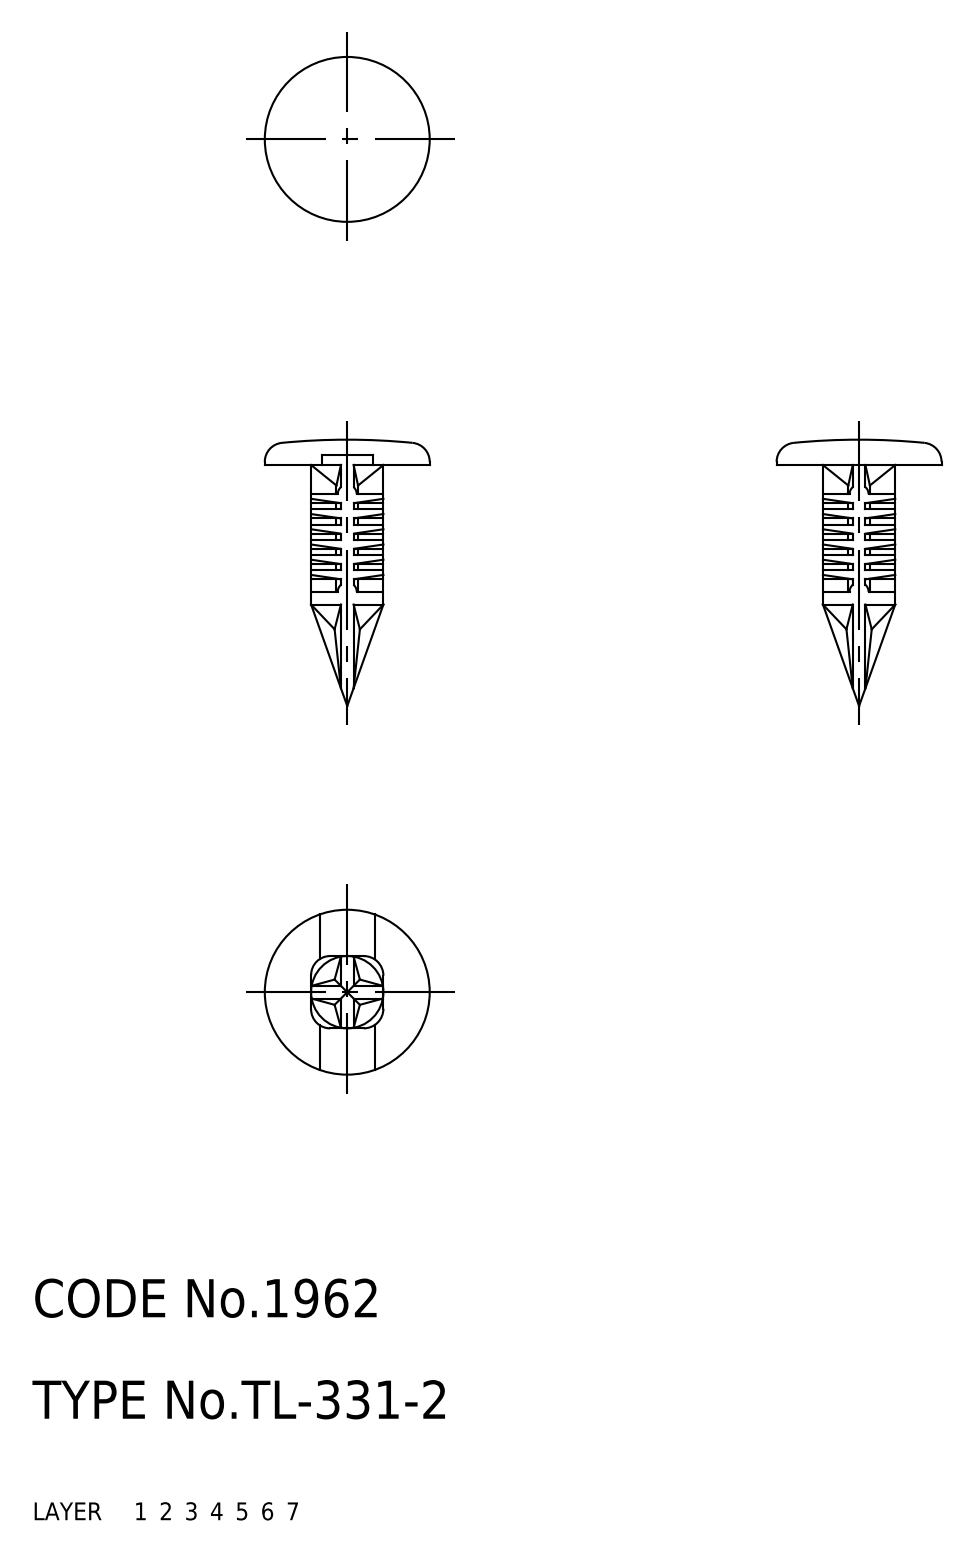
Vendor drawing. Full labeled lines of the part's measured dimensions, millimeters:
Part name (STEP PRODUCT): fastener
STEP written by: CADfix (AUTOMOTIVE_DESIGN)
Units: millimetres
Bodies: 1 solid, 219 faces (0 planar, 0 cylindrical, 219 other)
Overall size (bounding box): 21 × 13 × 12.8
Volume: 471 mm³ · Surface area: 885 mm²
